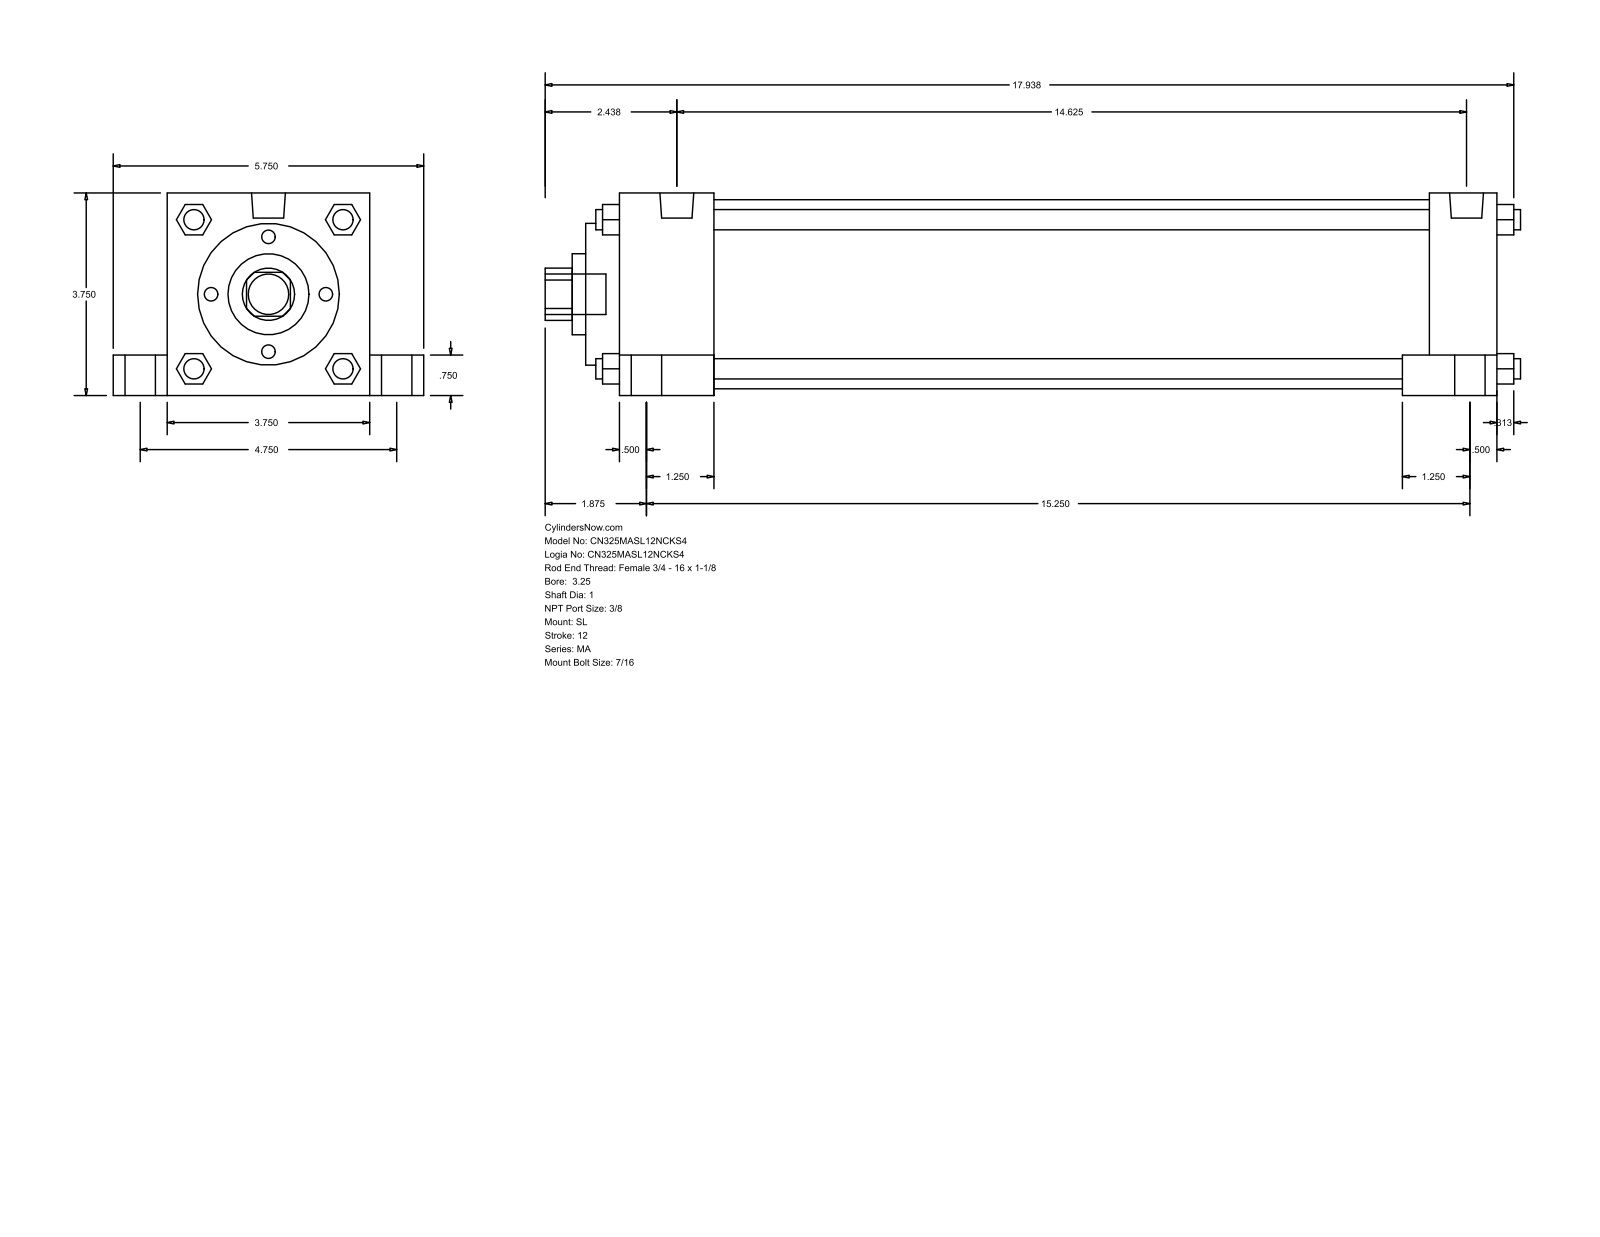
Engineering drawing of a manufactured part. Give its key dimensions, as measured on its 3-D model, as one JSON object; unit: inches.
{"part_name": "MA_SL__0325_1", "step_written_by": "GSSL Pune (CONFIG_CONTROL_DESIGN)", "units": "inches", "bodies": {"solids": 0, "faces": 150, "planar": 113, "cylindrical": 37, "other": 0}, "overall_size": [18.063, 5.75, 3.75], "round_holes": [[1, 1], [1.5, 1], [2.625, 1], [3.5, 1]], "round_bosses_or_shafts": [[0.813, 4], [0.563, 4], [0.437, 4], [0.375, 4], [0.627, 2], [0.75, 1]], "partial_cylinders_radius": [[0.484, 1]], "face_to_face_distances": [3.75, 16.25, 13.25, 0.625, 1, 4.75, 0.75, 15, 1.25, 1.75]}
